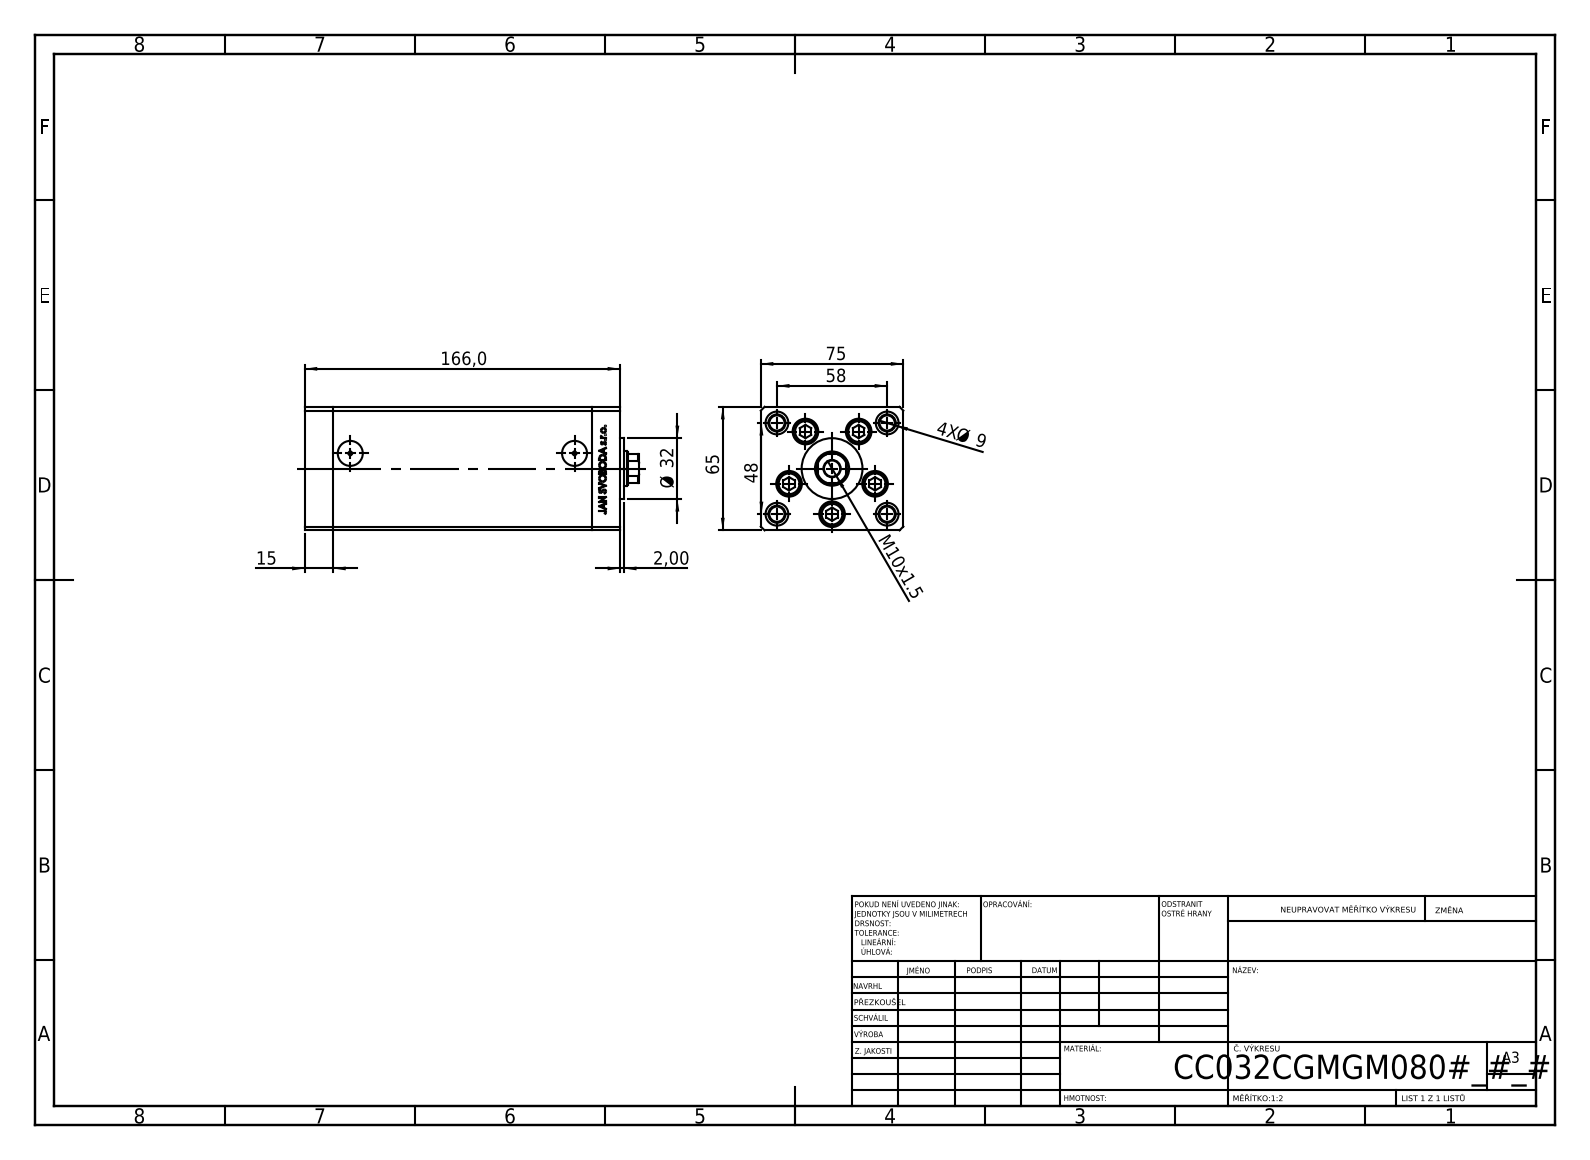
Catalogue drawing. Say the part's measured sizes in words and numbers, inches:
The part is named "V220C BACK_C; ALLEN BOLT; V220C_VC_C; V220C_C MIDDLE (+1 more)". Its 3-D file was written by "SolidWorks 2019 (CONFIG_CONTROL_DESIGN)". It is 13 solids with 1169 faces: 540 planar, 167 cylindrical and 462 other. Overall it measures 6.929 by 2.953 by 2.559 inches. Its volume is 41.53 cubic inches and its surface area 220.9 square inches. Round holes: 9 of diameter 0.354, 5 of diameter 0.531, 4 of diameter 0.315, 4 of diameter 0.472, 2 of diameter 0.079, 2 of diameter 0.518, 1 of diameter 0.335, 1 of diameter 0.492, 1 of diameter 0.709. Round bosses or shafts: 5 of diameter 0.315, 4 of diameter 0.492, 1 of diameter 1.26. Partial cylindrical surfaces (rounded edges, fillets, slot ends): 2 of radius 0.037, 1 of radius 0.335. The main face-to-face distances are 2.953, 2.559, 0.591, 5.354, 5.945, 6.535, 1.102, 5.591, 0.512, 0.354. The hole center spacings are 0.945, 1.482, 0.617, 0.678, 1.091, 1.135, 1.142, 1.285.
